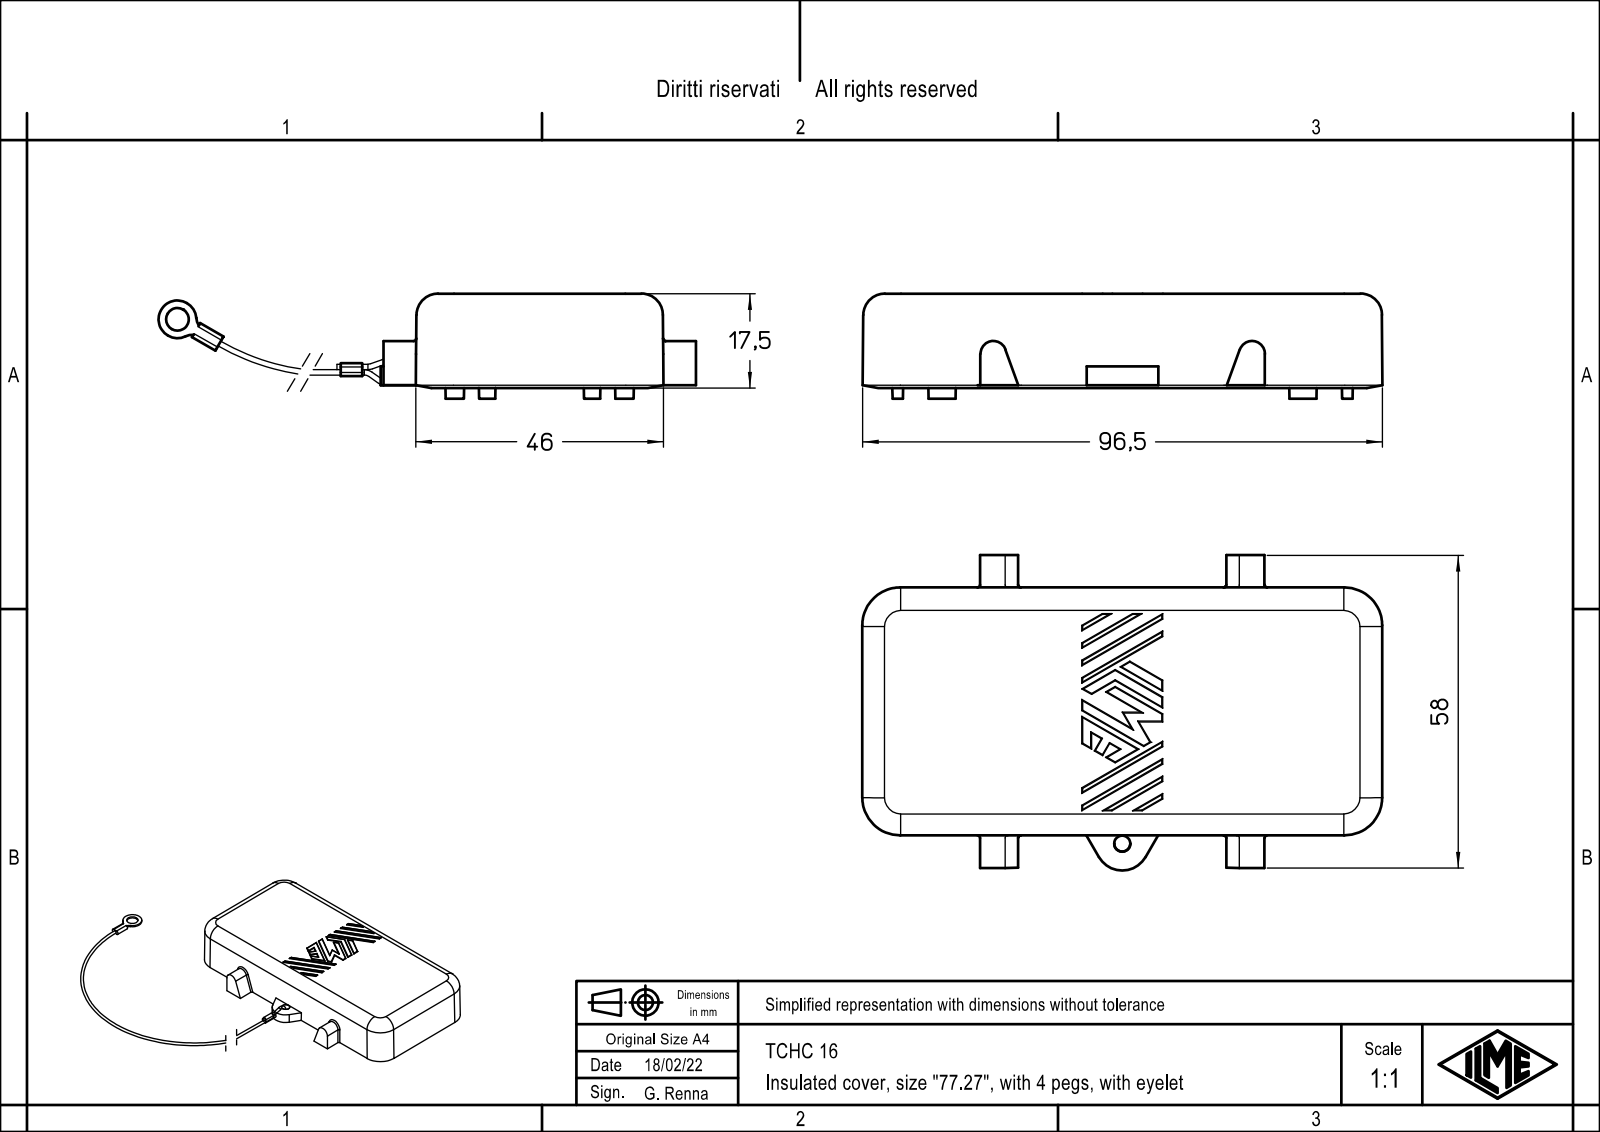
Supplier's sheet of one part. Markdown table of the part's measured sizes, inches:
| quantity | value |
| --- | --- |
| part name | TCHC_16 |
| STEP written by | Creo Elements/Direct Modeling 20.1B 02-Apr-2019 (C) Parametric Technology GmbH (AUTOMOTIVE_DESIGN) |
| units | inches |
| bodies | 1 solid, 278 faces (117 planar, 114 cylindrical, 47 other) |
| overall size | 8.987 × 3.799 × 0.774 |
| volume | 2.574 in³ |
| surface area | 27.91 in² |
| round holes (diameter × count) | 0.118 × 1, 0.165 × 1 |
| round bosses / shafts (diameter × count) | 0.039 × 4, 0.276 × 1 |
| partial cylindrical surfaces (radius × count) | 0.006 × 44, 0.059 × 4, 0.157 × 4, 0.276 × 4, 0.028 × 2, 0.03 × 2, 0.049 × 2, 0.094 × 2 |
| main face-to-face distances | 0.217, 0.217, 0.276, 0.452, 0.669, 0.275, 0.675, 0.222, 0.621, 0.768 |
| hole center spacings | 5.128 |
